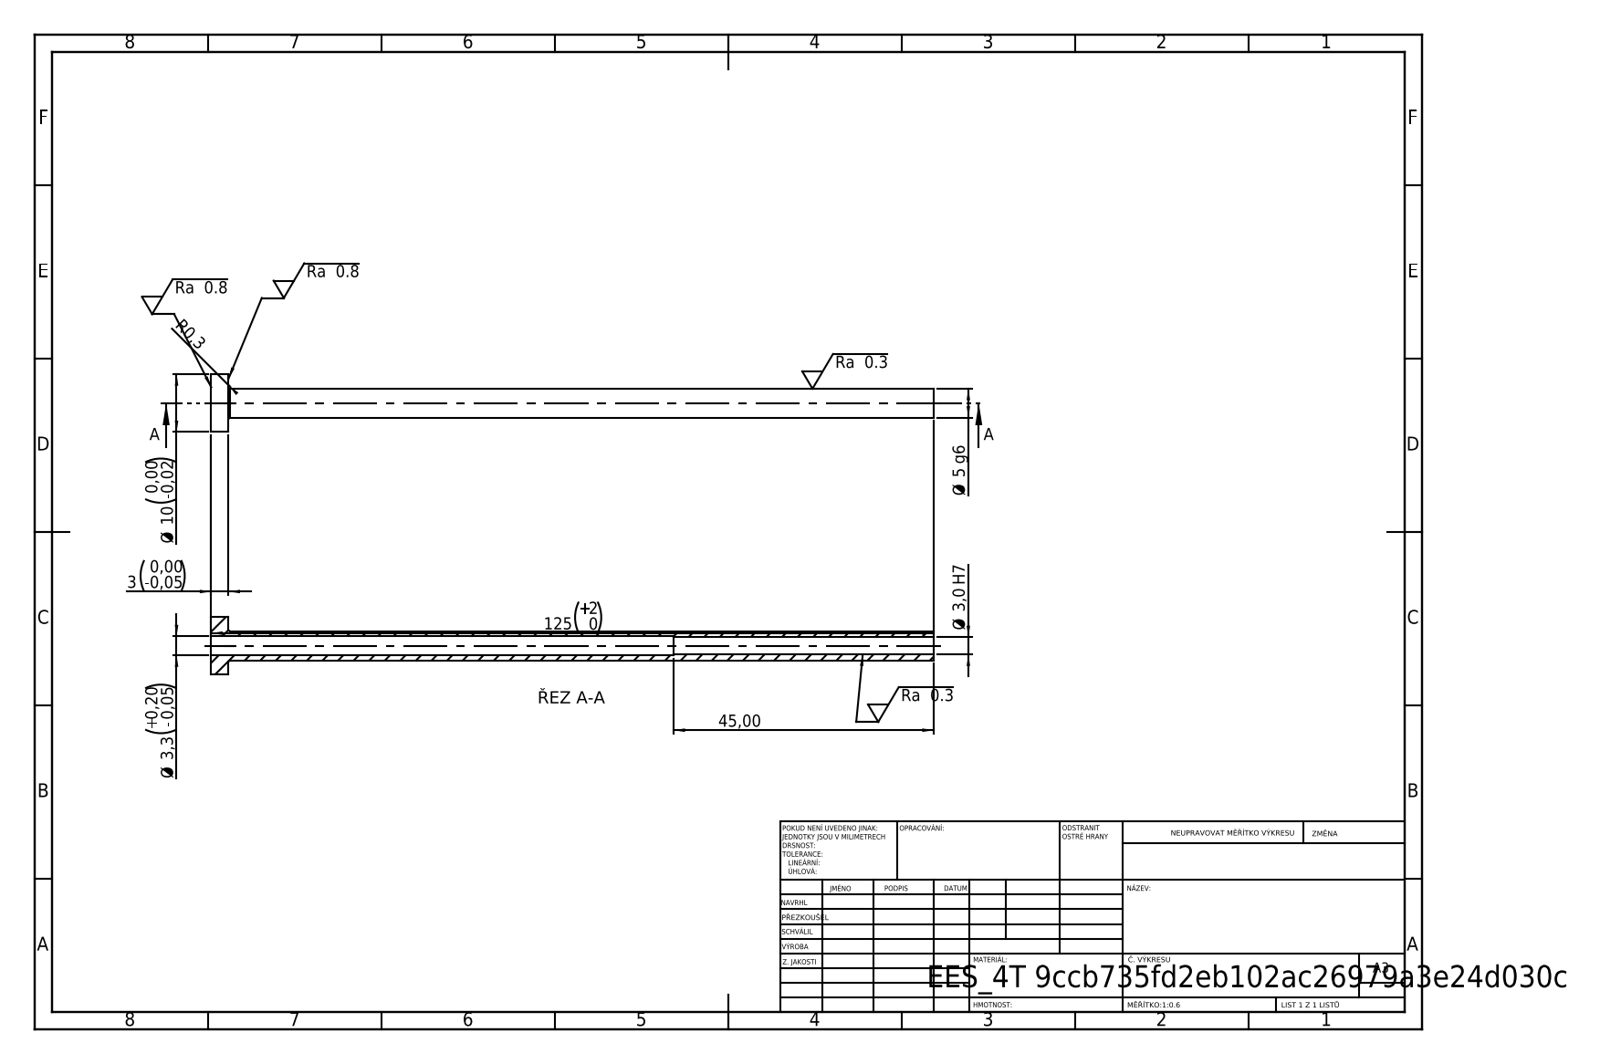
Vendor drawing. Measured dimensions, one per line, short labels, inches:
written by: SolidWorks 2019 (CONFIG_CONTROL_DESIGN)
unit: in
bodies: 1 solid, 14 faces (4 planar, 8 cylindrical, 2 other)
size: 4.921 × 0.394 × 0.394
volume: 0.099 in³; area: 5.278 in²
holes: 1× ⌀0.118, 1× ⌀0.13
bosses: 1× ⌀0.394, 1× ⌀0.197
face distances: 0.118, 4.921, 4.803, 3.15, 3.031, 1.772
